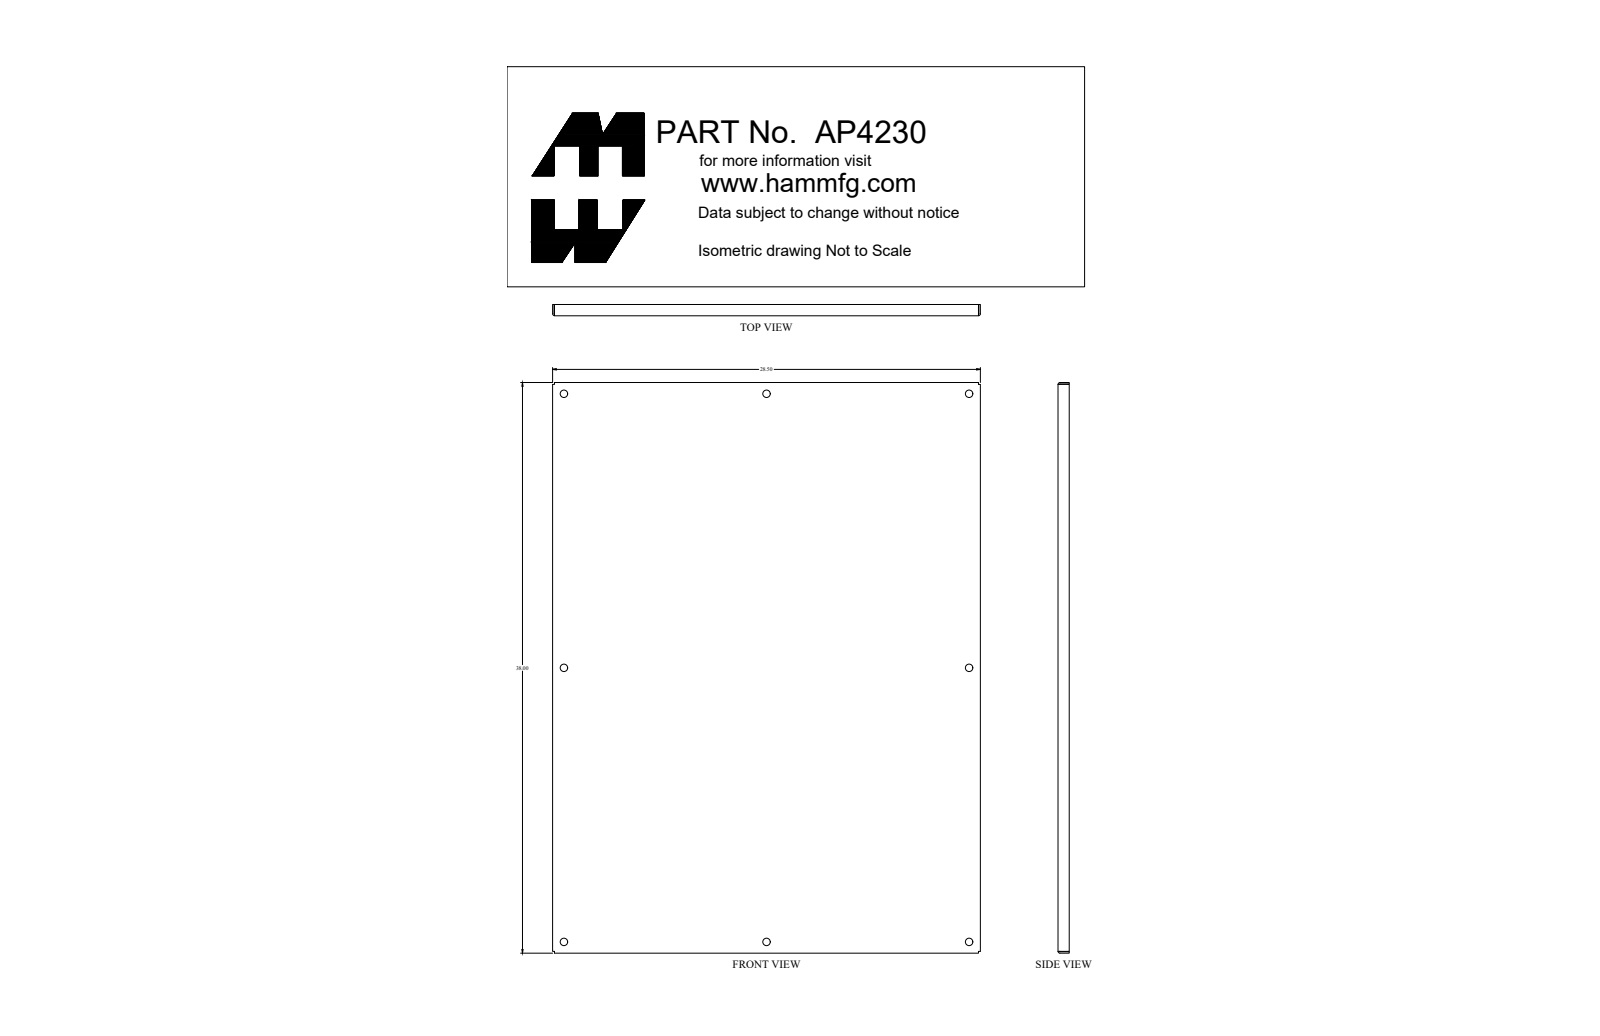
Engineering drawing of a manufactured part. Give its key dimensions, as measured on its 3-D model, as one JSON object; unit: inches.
{"part_name": "AP4230_Default", "step_written_by": "SolidWorks 2019 (CONFIG_CONTROL_DESIGN)", "units": "inches", "bodies": {"solids": 1, "faces": 46, "planar": 22, "cylindrical": 24, "other": 0}, "overall_size": [38, 28.5, 0.75], "volume_in3": 110.5, "surface_area_in2": 2341, "round_holes": [[0.5, 8]], "partial_cylinders_radius": [[0.03, 4], [0.125, 4]], "face_to_face_distances": [0.095, 28.405, 37.905, 28.31, 28.5, 38, 37.81, 0.75, 0.655, 0.125], "hole_center_spacings": [13.499, 18.249, 22.699, 32.587, 38.914, 26.998, 36.498, 45.398]}
